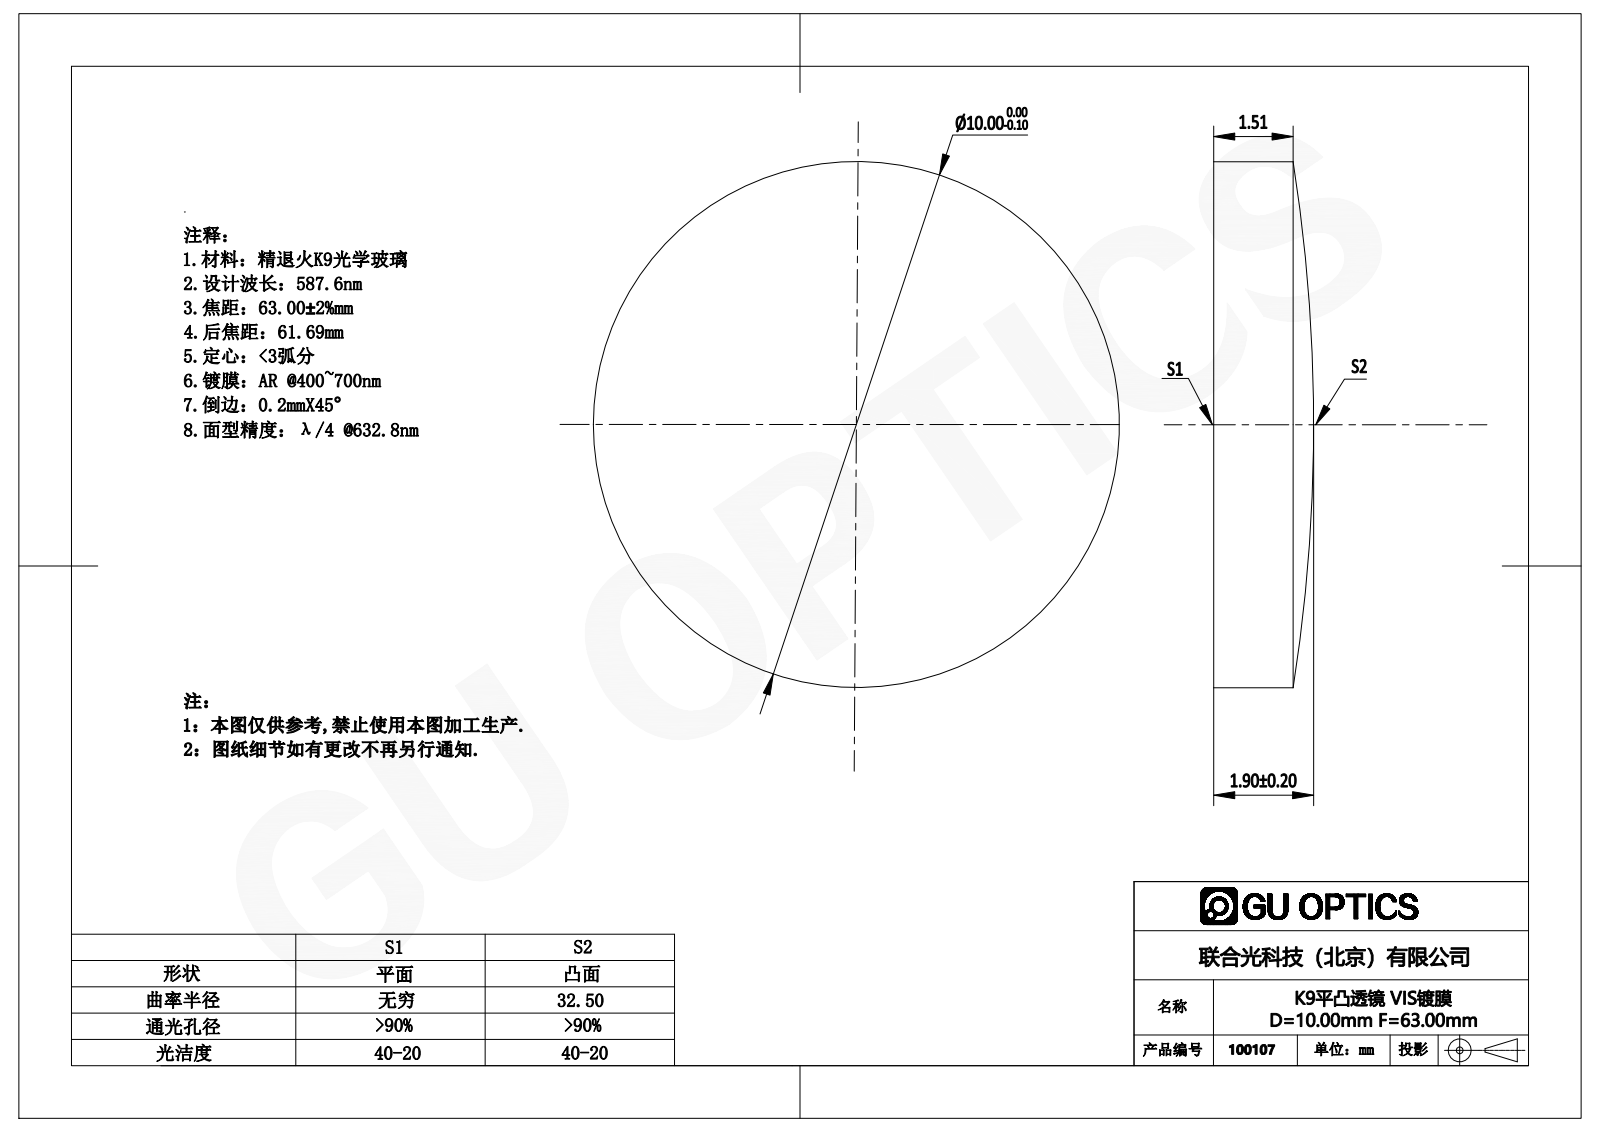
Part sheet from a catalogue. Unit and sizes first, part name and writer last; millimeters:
Units: millimetres
Overall size (bounding box): 10 × 10 × 1.9
Round bosses / shafts (diameter × count): ⌀10 ×1
Volume: 134 mm³ · Surface area: 205 mm²
Bodies: 1 solid, 5 faces (1 planar, 2 cylindrical, 2 other)
Part name (STEP PRODUCT): 100107
STEP written by: SolidWorks 2016 (AUTOMOTIVE_DESIGN)
